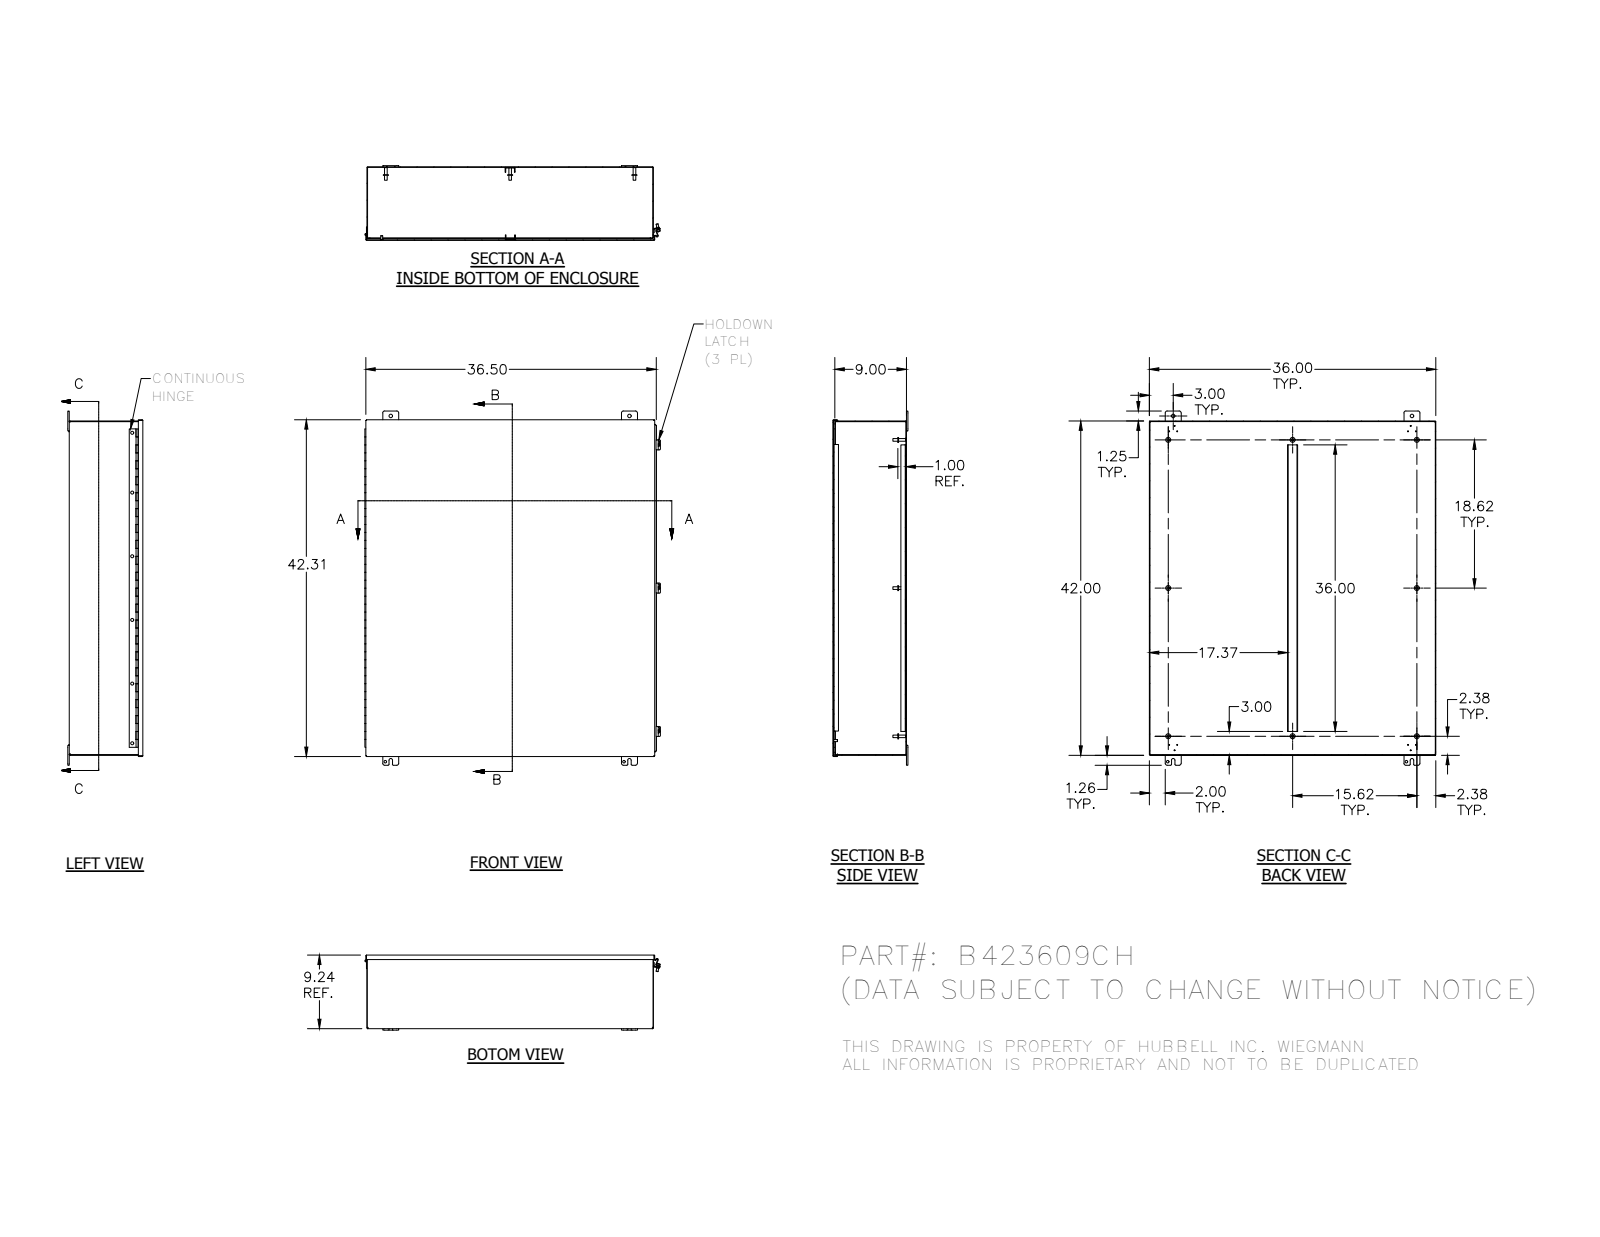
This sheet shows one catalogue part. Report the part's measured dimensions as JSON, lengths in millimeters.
{"part_name": "B423609CH; B423609CHBKP; B4236CHLID; H6010104 (+8 more)", "step_written_by": "Autodesk Inventor 2012 (AUTOMOTIVE_DESIGN)", "units": "millimeters", "bodies": {"solids": 29, "faces": 930, "planar": 583, "cylindrical": 267, "other": 80}, "overall_size": [1130.4, 943.3, 239.3], "volume_mm3": 5909000, "surface_area_mm2": 6294000, "round_holes": [[2.8, 6], [9.5, 6], [8, 4], [11.1, 4], [5, 3], [3.2, 1], [3.2, 1]], "round_bosses_or_shafts": [[15.9, 8], [8.4, 8], [6.4, 5], [10.4, 3], [8.7, 3], [8.6, 1], [3, 1]], "partial_cylinders_radius": [[3.2, 20], [6.4, 16], [1.6, 12], [1.6, 11], [0.8, 8], [1.8, 8], [2.7, 8], [3.4, 6]], "face_to_face_distances": [1.9, 232.9, 231, 234.8, 912.5, 1064.9, 914.4, 910.6, 1063, 1066.8], "hole_center_spacings": [457.2, 762, 19.1, 40.5, 203.2, 1066.9, 1311.1, 28.8]}
